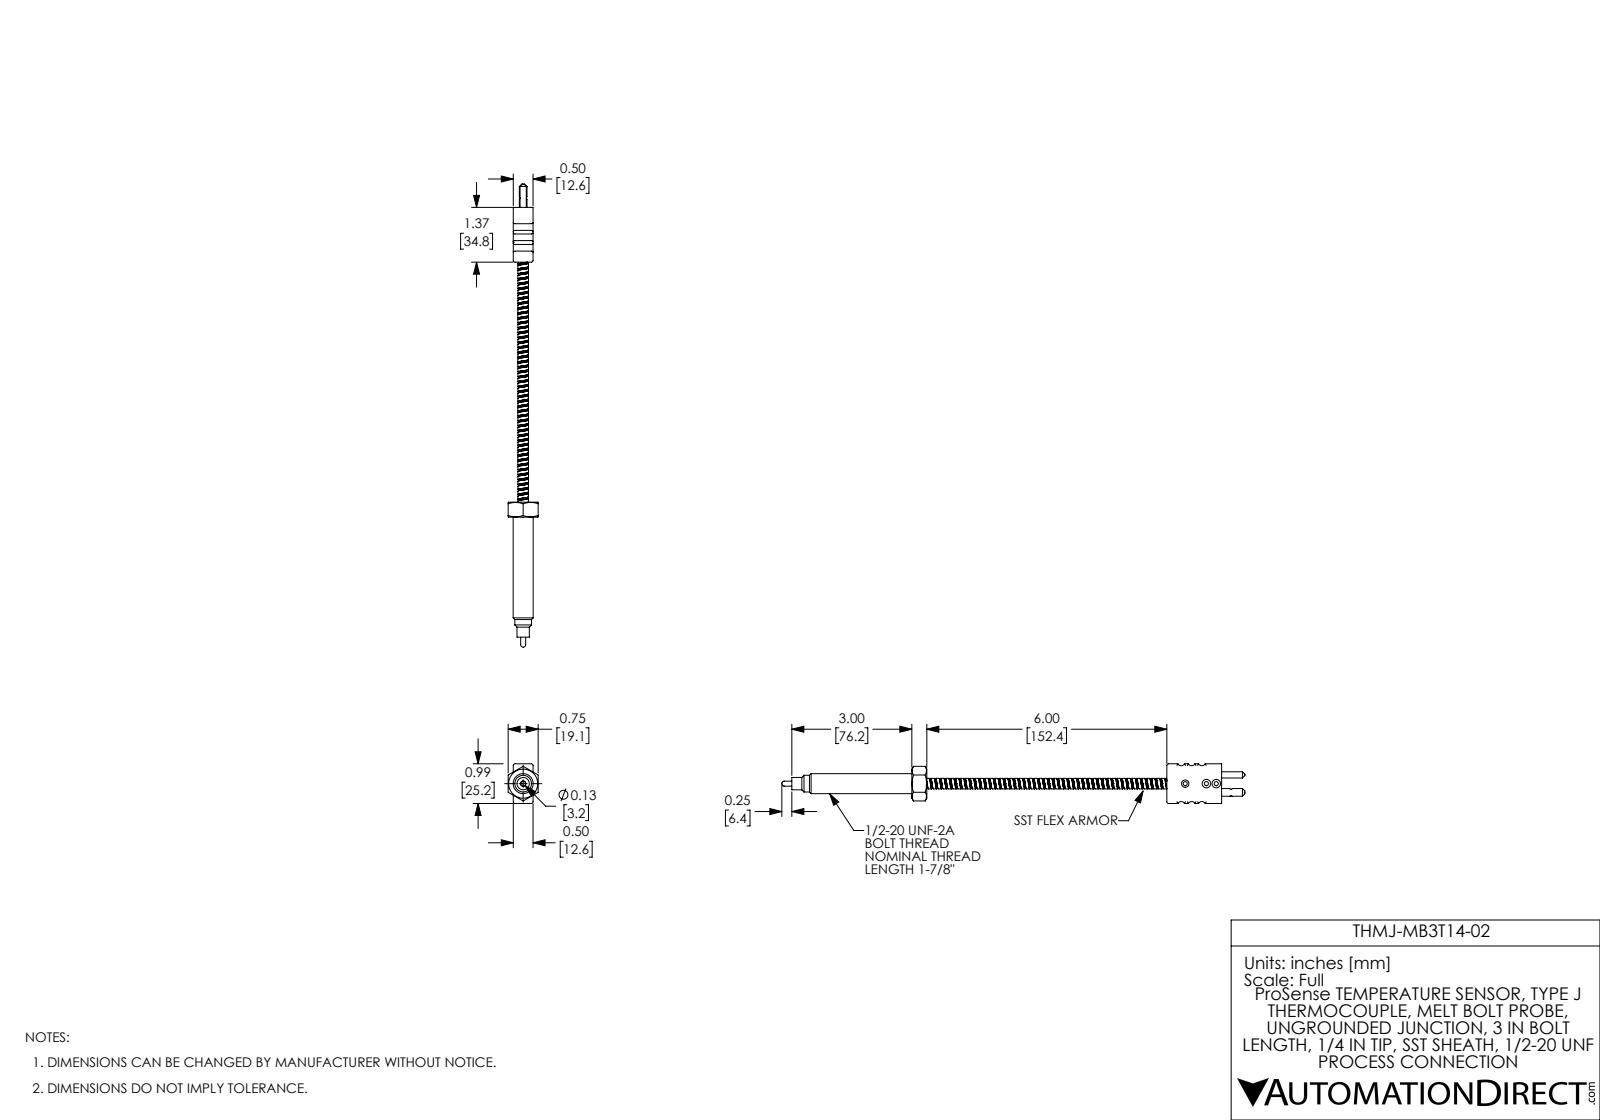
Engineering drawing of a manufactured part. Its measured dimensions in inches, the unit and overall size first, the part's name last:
Units: inches
Overall size (bounding box): 11.576 × 0.993 × 0.75
Round holes (diameter × count): ⌀0.103 ×2, ⌀0.158 ×2, ⌀0.135 ×1, ⌀0.185 ×1, ⌀0.294 ×1, ⌀0.308 ×1
Round bosses / shafts (diameter × count): ⌀0.5 ×1, ⌀0.417 ×1, ⌀0.309 ×1, ⌀0.278 ×1, ⌀0.265 ×1, ⌀0.191 ×1, ⌀0.156 ×1, ⌀0.125 ×1
Partial cylindrical surfaces — rounded edges, fillets, slot ends (radius × count): R0.045 ×8, R0.095 ×6, R0.01 ×4
Main face-to-face distances: 0.495, 0.75, 7.369, 0.993, 0.127, 0.622, 1.369, 6, 7.744, 6.375
Hole centre spacings: 0.217, 0.328, 0.572, 0.247, 0.433, 0.529, 0.776
Volume: 1.685 in³ · Surface area: 19.21 in²
Bodies: 3 solids, 312 faces (69 planar, 172 cylindrical, 71 other)
Part name (STEP PRODUCT): THMJ-MB3T14-02
STEP written by: SolidWorks 2017 (AUTOMOTIVE_DESIGN)
